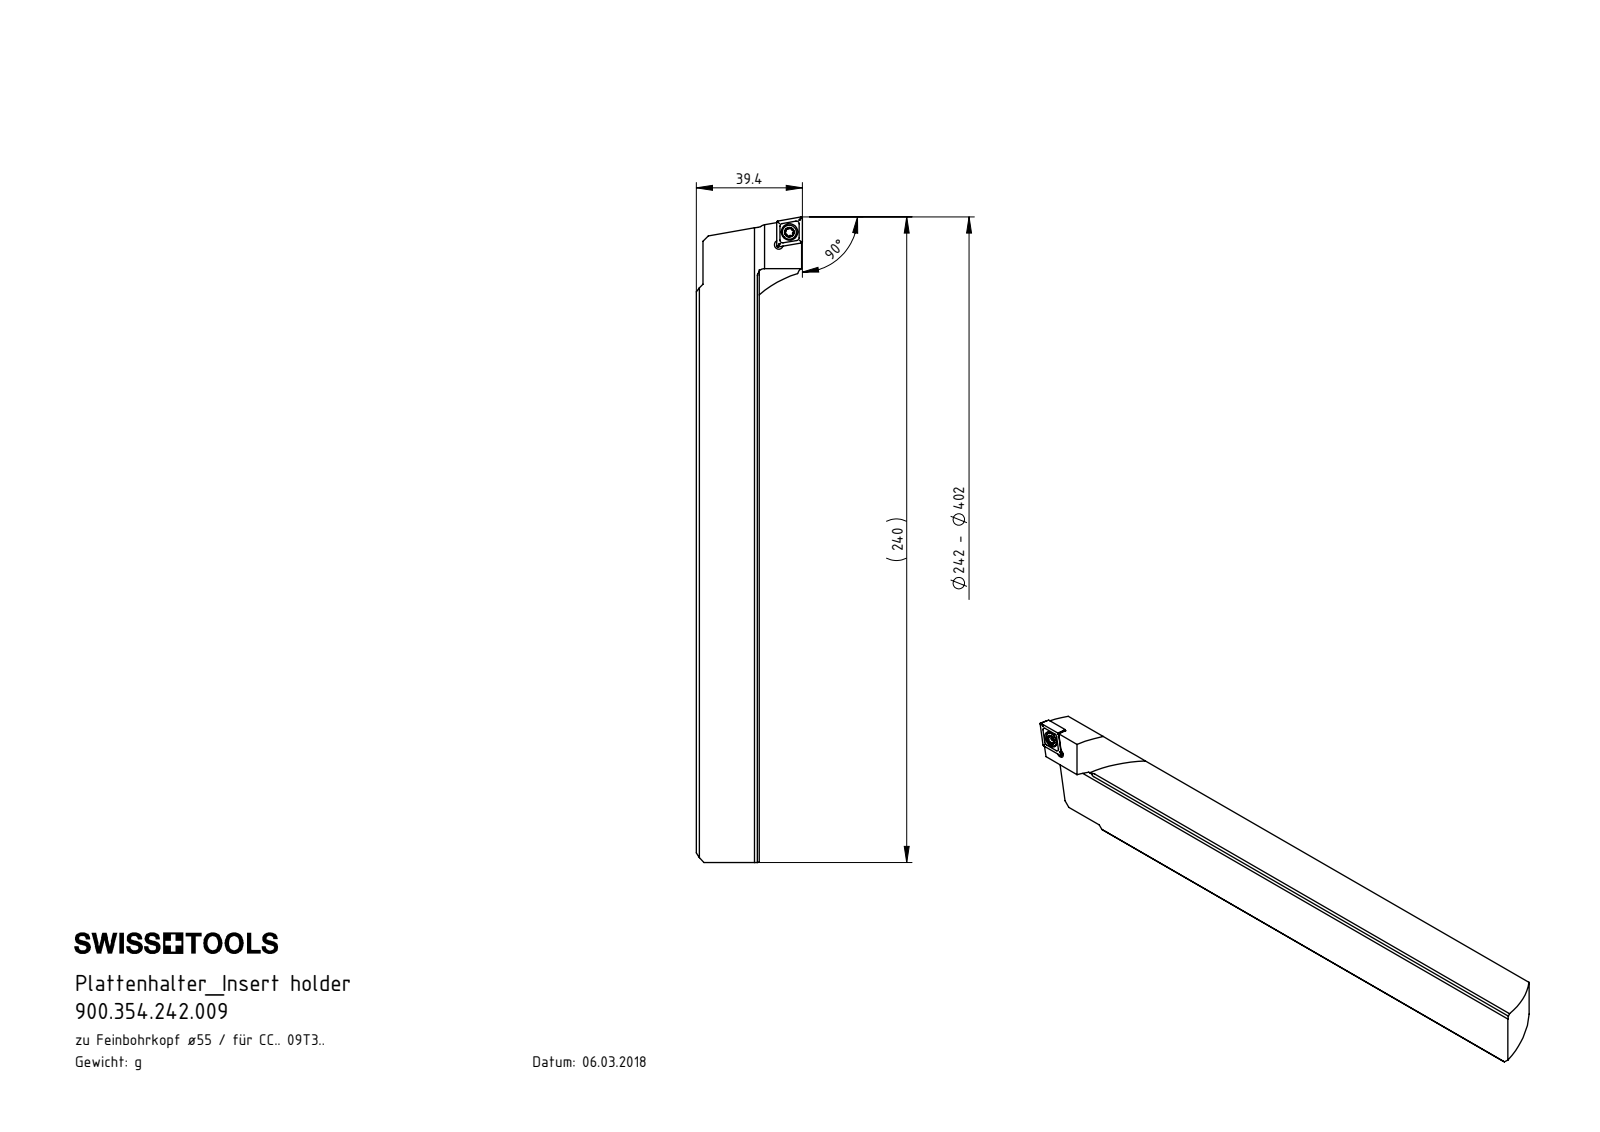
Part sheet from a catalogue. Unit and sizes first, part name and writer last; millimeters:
Units: millimetres
Overall size (bounding box): 239.57 × 39.4 × 27.35
Round holes (diameter × count): ⌀3.3 ×2, ⌀4.4 ×1, ⌀6.1 ×1
Round bosses / shafts (diameter × count): ⌀5.25 ×1, ⌀4 ×1
Partial cylindrical surfaces — rounded edges, fillets, slot ends (radius × count): R0.2 ×8, R0.34 ×6, R0.59 ×6, R40 ×3, R0.8 ×1
Main face-to-face distances: 2.38, 4.76, 21.3, 7.14, 9.52, 4.77, 7.15, 9.53, 11.91, 14.29
Hole centre spacings: 6.06, 6.19
Volume: 100 278 mm³ · Surface area: 24 143 mm²
Bodies: 3 solids, 916 faces (564 planar, 39 cylindrical, 313 other)
Part name (STEP PRODUCT): CCMT09T304; F00-WCB.242.001_C; 900.354.242.009; WCB-ER2.001.009_A
STEP written by: SolidWorks 2017 (CONFIG_CONTROL_DESIGN)
